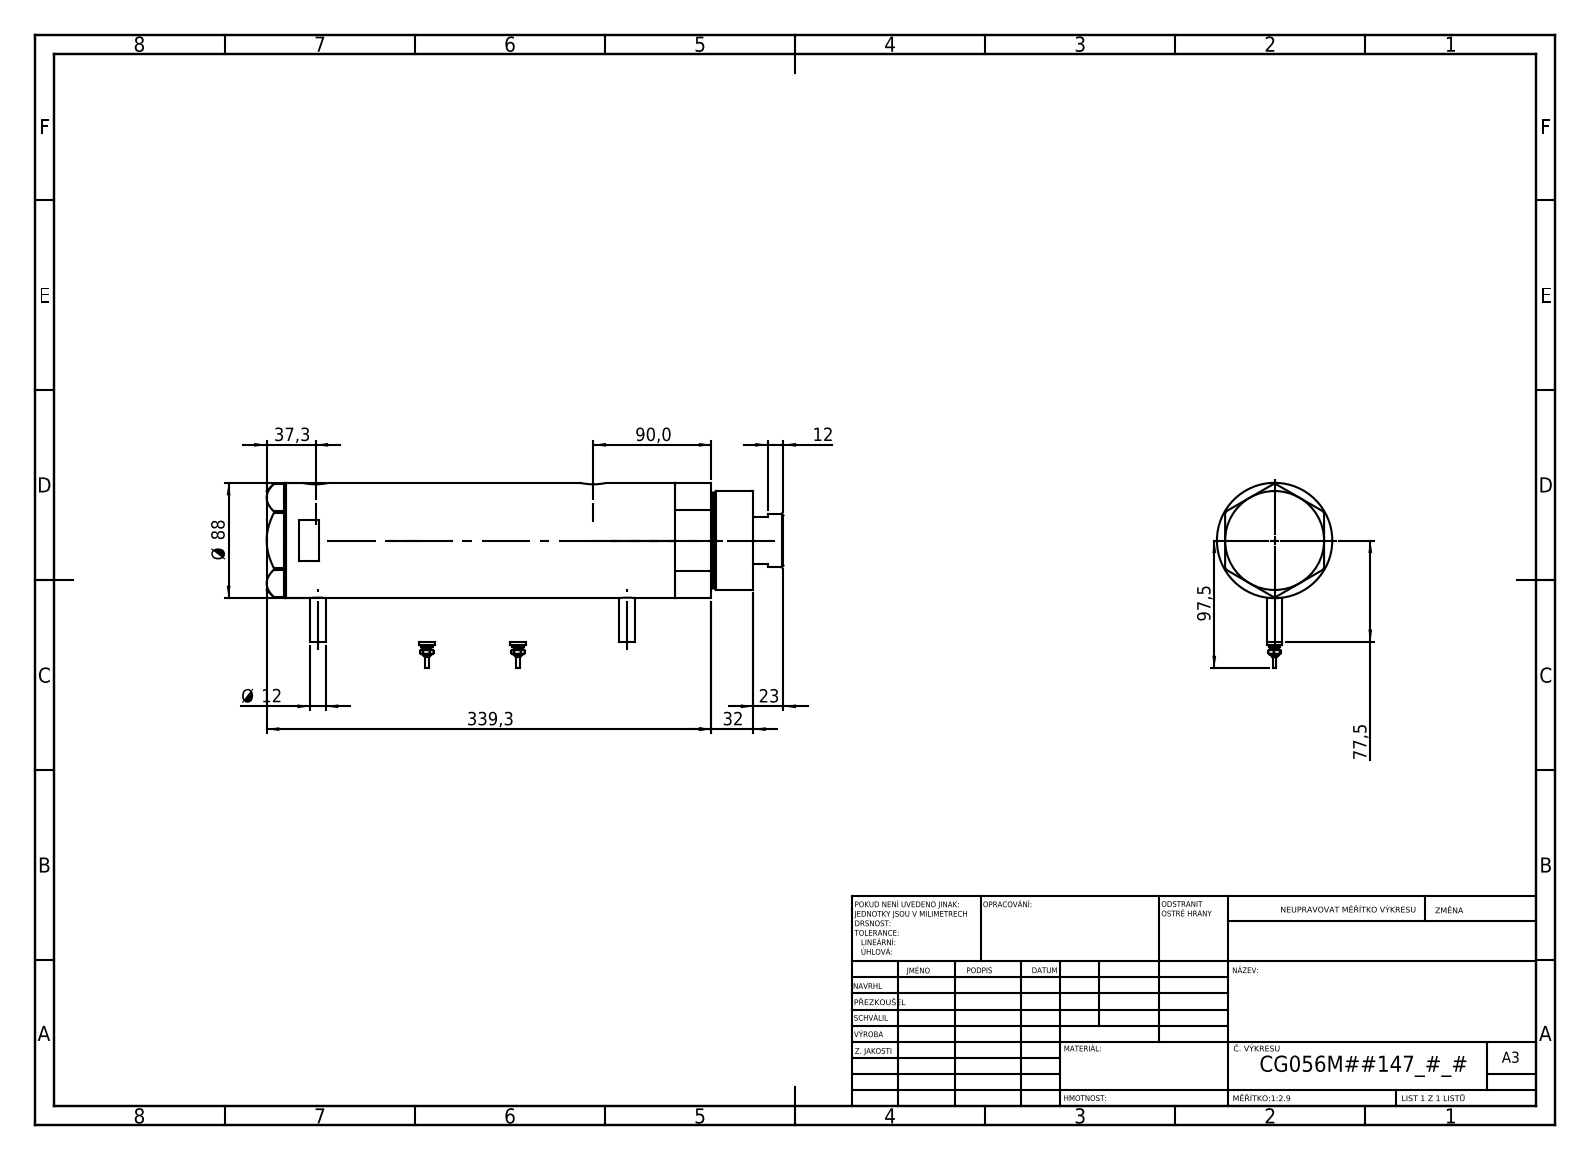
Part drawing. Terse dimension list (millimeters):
name: V270CG_BACK; V270CG_FRONT; Switch; V270CG_VC (+1 more)
written by: SolidWorks 2019 (CONFIG_CONTROL_DESIGN)
unit: mm
bodies: 6 solids, 213 faces (80 planar, 69 cylindrical, 64 other)
size: 394.3 × 141.5 × 88
volume: 2 045 000 mm³; area: 283 155 mm²
holes: 2× ⌀12.5, 2× ⌀13.16, 2× ⌀20, 1× ⌀14.5, 1× ⌀42, 1× ⌀43.5, 1× ⌀56, 1× ⌀60, 1× ⌀80
bosses: 4× ⌀12, 2× ⌀9, 2× ⌀7, 2× ⌀4.5, 2× ⌀2.5, 1× ⌀88, 1× ⌀75, 1× ⌀73
face distances: 234.4, 26, 208.4, 15, 41, 249.4, 356.3, 371.3, 330.3, 121.9
hole spacings: 1.7, 25.8, 210.3, 212, 236.1, 237.8
